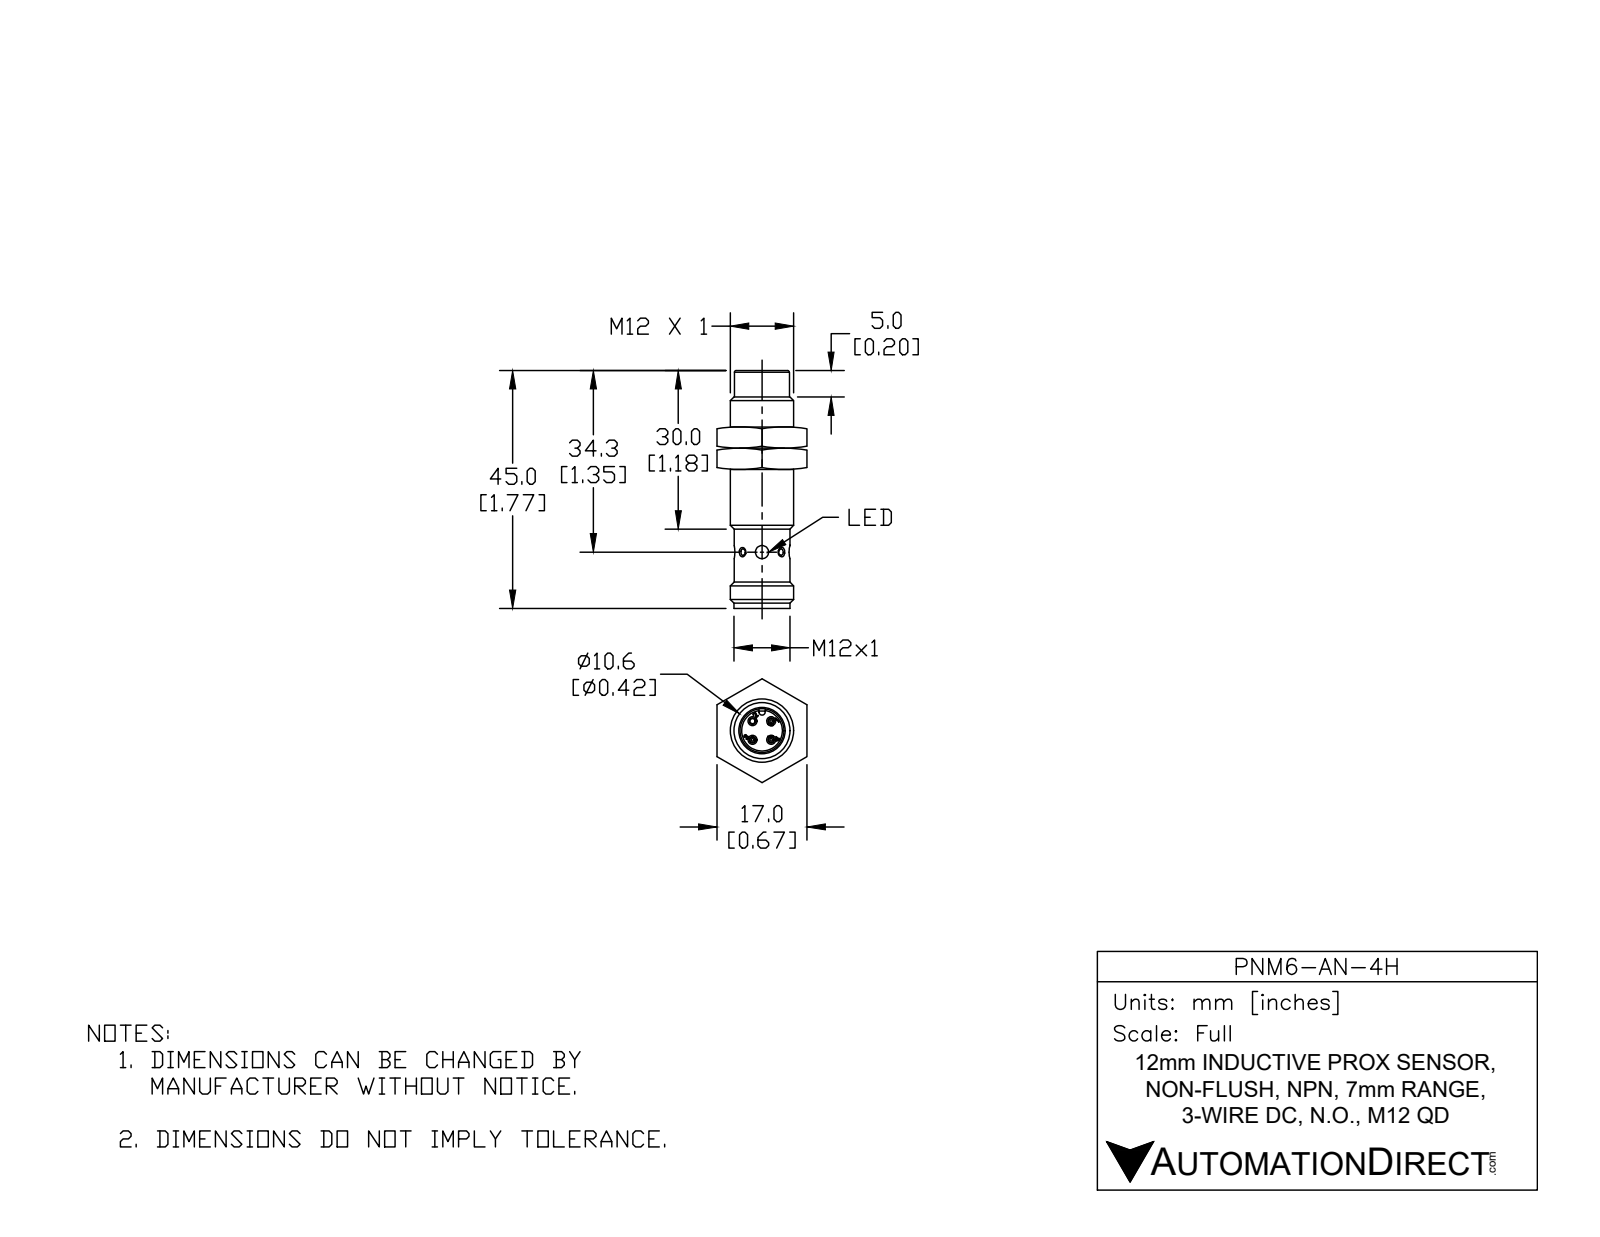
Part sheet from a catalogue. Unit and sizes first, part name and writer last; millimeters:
Units: millimetres
Overall size (bounding box): 45 × 12 × 12
Round holes (diameter × count): ⌀1.1 ×3, ⌀1 ×2, ⌀2.5 ×2, ⌀1 ×1, ⌀1 ×1, ⌀8.3 ×1, ⌀10 ×1, ⌀10.2 ×1
Round bosses / shafts (diameter × count): ⌀1 ×6, ⌀12 ×1, ⌀10.6 ×1, ⌀10.5 ×1, ⌀10.2 ×1, ⌀10 ×1, ⌀9.9 ×1, ⌀9.7 ×1
Partial cylindrical surfaces — rounded edges, fillets, slot ends (radius × count): R0.1 ×36, R2 ×6, R0.6 ×1, R0.8 ×1, R4.1 ×1
Main face-to-face distances: 3, 33, 30, 0.5, 2.5, 32.5, 33.1, 36.1, 35.7, 3.1
Hole centre spacings: 2.5, 3.5, 5
Volume: 4 050 mm³ · Surface area: 5 172 mm²
Bodies: 1 solid, 491 faces (117 planar, 138 cylindrical, 236 other)
Part name (STEP PRODUCT): PNM6-AN-4H
STEP written by: SolidWorks 2017 (AUTOMOTIVE_DESIGN)
